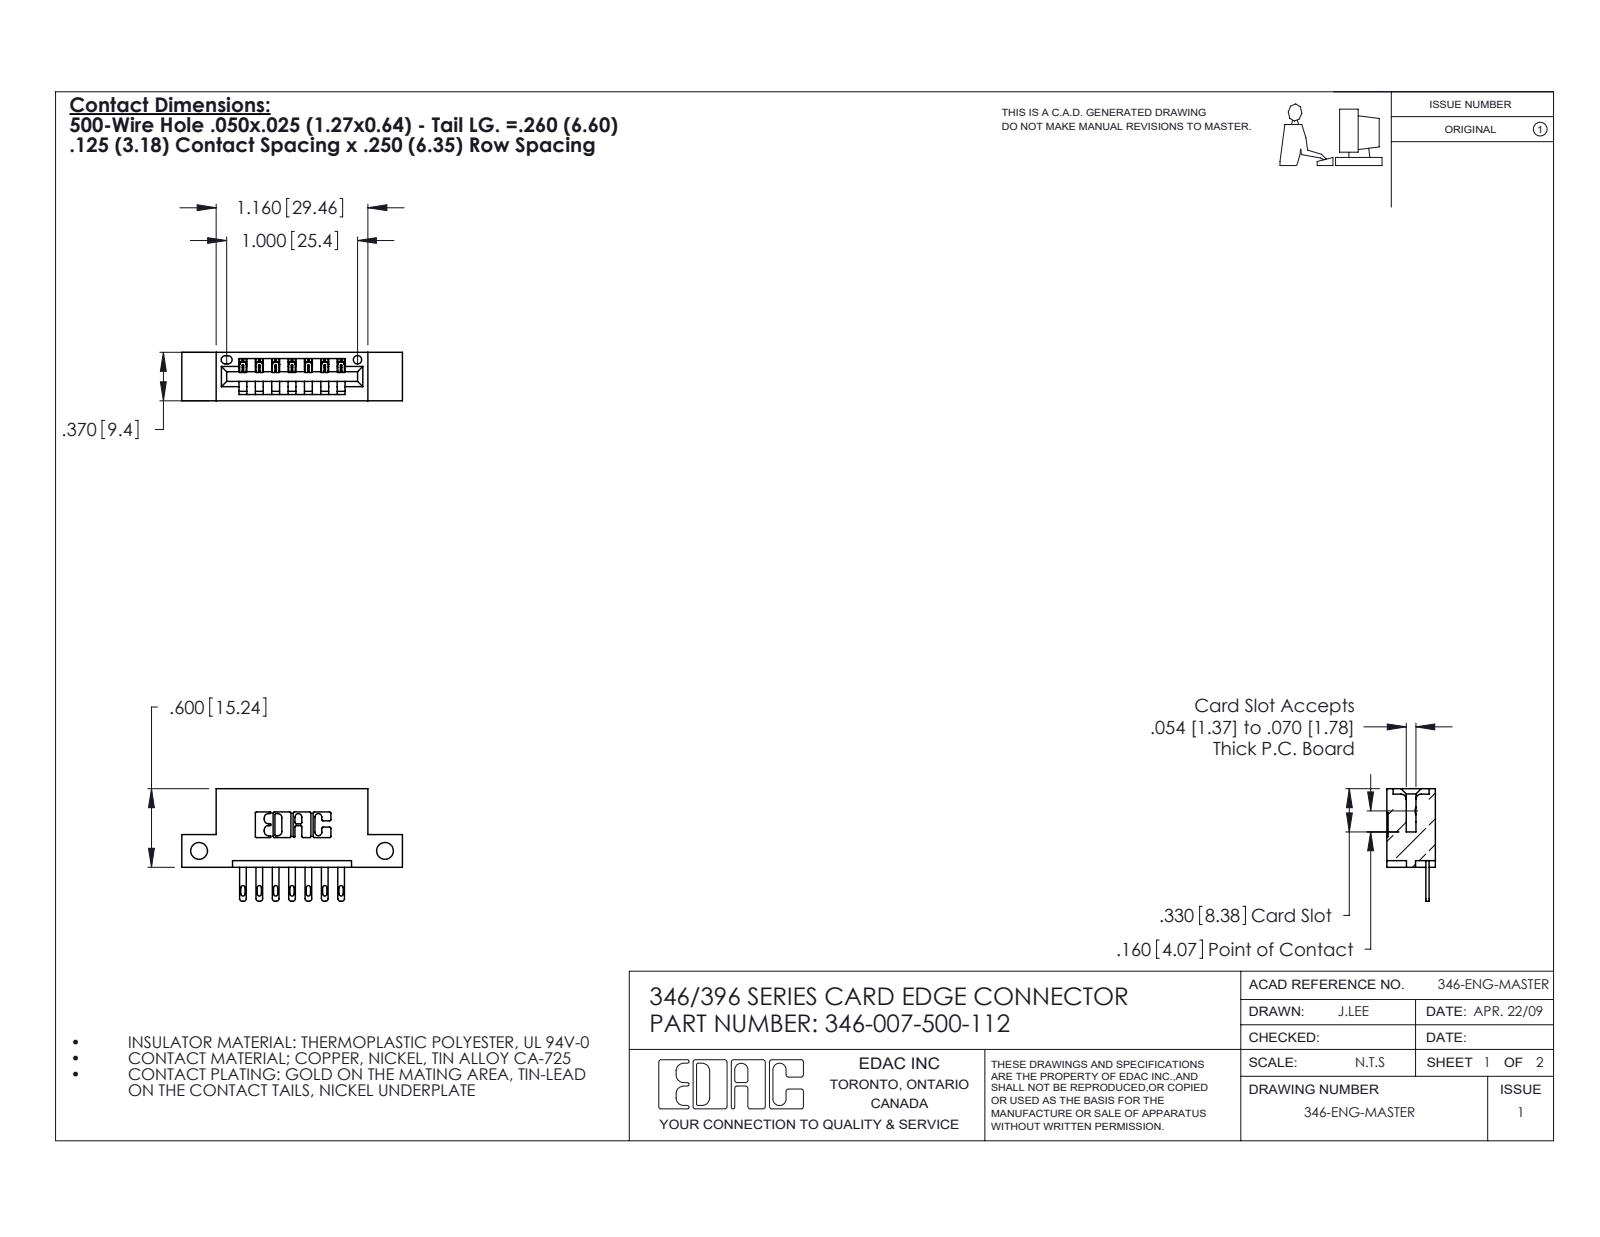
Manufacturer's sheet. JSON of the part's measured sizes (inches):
{"part_name": "345-292-001_345-293-100; 346-007-500-112; 346 Part_Flush Mounting Lugs - Side Mount", "step_written_by": "SolidWorks 2020 (CONFIG_CONTROL_DESIGN)", "units": "inches", "bodies": {"solids": 8, "faces": 500, "planar": 314, "cylindrical": 186, "other": 0}, "overall_size": [1.685, 0.86, 0.37], "volume_in3": 0.23, "surface_area_in2": 6.523, "round_holes": [[0.128, 2], [0.064, 1]], "partial_cylinders_radius": [[0.01, 22], [0.006, 14], [0.016, 14], [0.02, 14], [0.007, 6], [0.031, 6], [0.026, 3], [0.031, 2]], "face_to_face_distances": [0.25, 0.37, 0.048, 0.322, 0.072, 0.298, 0.025, 0.148, 0.222, 0.1], "hole_center_spacings": [1.42]}
